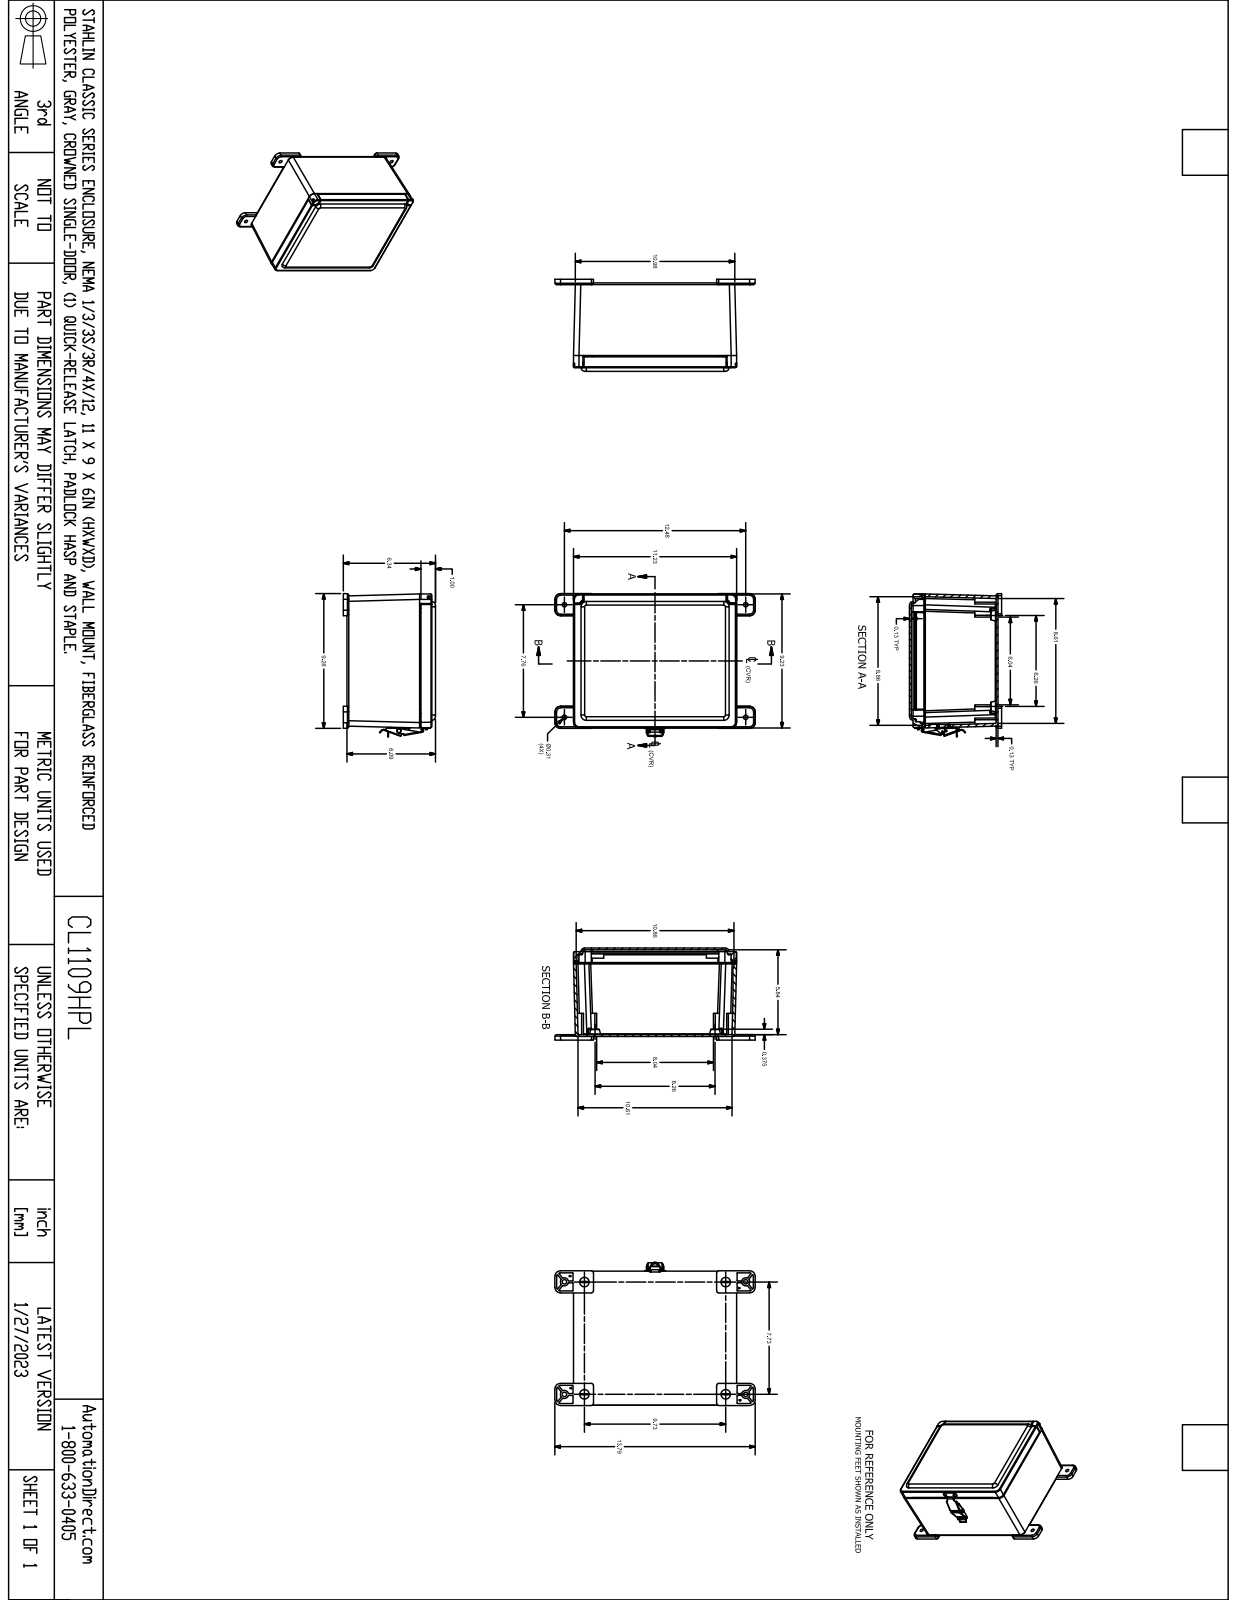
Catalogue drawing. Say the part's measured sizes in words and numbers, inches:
The part is named "CE1109HPL". Its 3-D file was written by "SolidWorks 2018 (AUTOMOTIVE_DESIGN)". It is 36 solids with 1588 faces: 690 planar, 497 cylindrical and 401 other. Overall it measures 13.793 by 9.872 by 6.344 inches. Its volume is 88.15 cubic inches and its surface area 1 035 square inches. Round holes: 6 of diameter 0.159, 6 of diameter 0.281, 4 of diameter 0.104, 4 of diameter 0.14, 4 of diameter 0.156, 4 of diameter 0.313, 4 of diameter 0.313, 4 of diameter 0.344, 4 of diameter 0.531, 2 of diameter 0.096, 2 of diameter 0.13, 2 of diameter 0.13. Round bosses or shafts: 6 of diameter 0.27, 5 of diameter 0.125, 4 of diameter 0.229, 2 of diameter 0.375, 1 of diameter 0.325, 1 of diameter 0.3, 1 of diameter 0.299, 1 of diameter 0.185. Partial cylindrical surfaces (rounded edges, fillets, slot ends): 60 of radius 0.031, 56 of radius 0.031, 42 of radius 0.125, 17 of radius 0.062, 16 of radius 0.25, 13 of radius 0.063, 13 of radius 0.1, 10 of radius 0.375. The main face-to-face distances are 0.125, 5.969, 0.186, 6.094, 5.844, 0.25, 0.125, 0.75, 5.844, 5.719. The hole center spacings are 0.75, 1.039, 1.375, 2.238, 7.035, 7.32, 7.489, 7.865.
